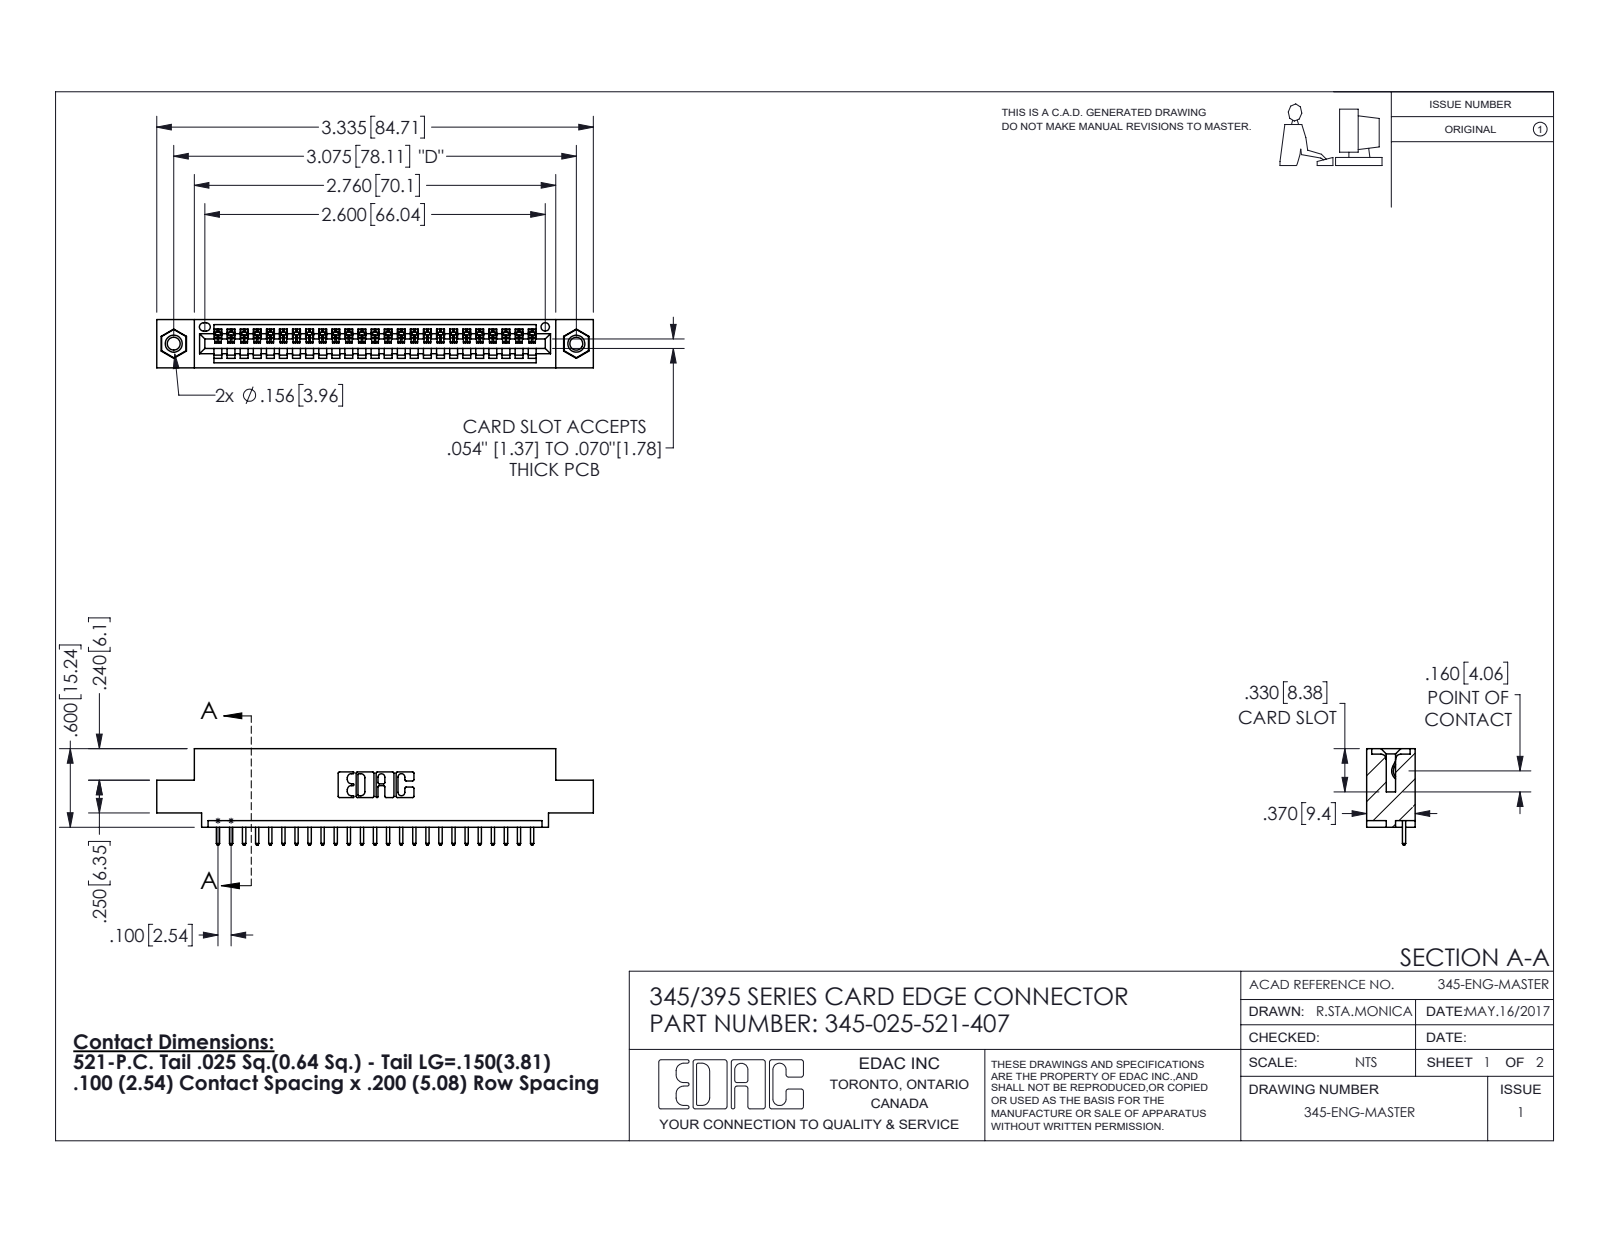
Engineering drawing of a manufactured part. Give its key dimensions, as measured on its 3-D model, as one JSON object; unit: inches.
{"part_name": "345 Part_0.110 Offset - 0.156 Dia-TI; 345-025-521-407; 345-250-001_345-250-005-103; 345-292-001_345-293-121", "step_written_by": "SolidWorks 2016 (CONFIG_CONTROL_DESIGN)", "units": "inches", "bodies": {"solids": 28, "faces": 1640, "planar": 1116, "cylindrical": 508, "other": 16}, "overall_size": [3.335, 0.737, 0.37], "volume_in3": 0.473, "surface_area_in2": 15.35, "round_holes": [[0.098, 2], [0.125, 2], [0.156, 2], [0.064, 1]], "round_bosses_or_shafts": [[0.155, 2]], "partial_cylinders_radius": [[0.006, 50], [0.01, 50], [0.01, 22], [0.007, 6], [0.031, 6], [0.026, 3], [0.031, 2], [0.04, 2]], "face_to_face_distances": [0.072, 0.298, 0.37, 0.2, 0.098, 0.272, 0.025, 0.225, 0.149, 0.072], "hole_center_spacings": [0.27, 2.84, 3.075]}
